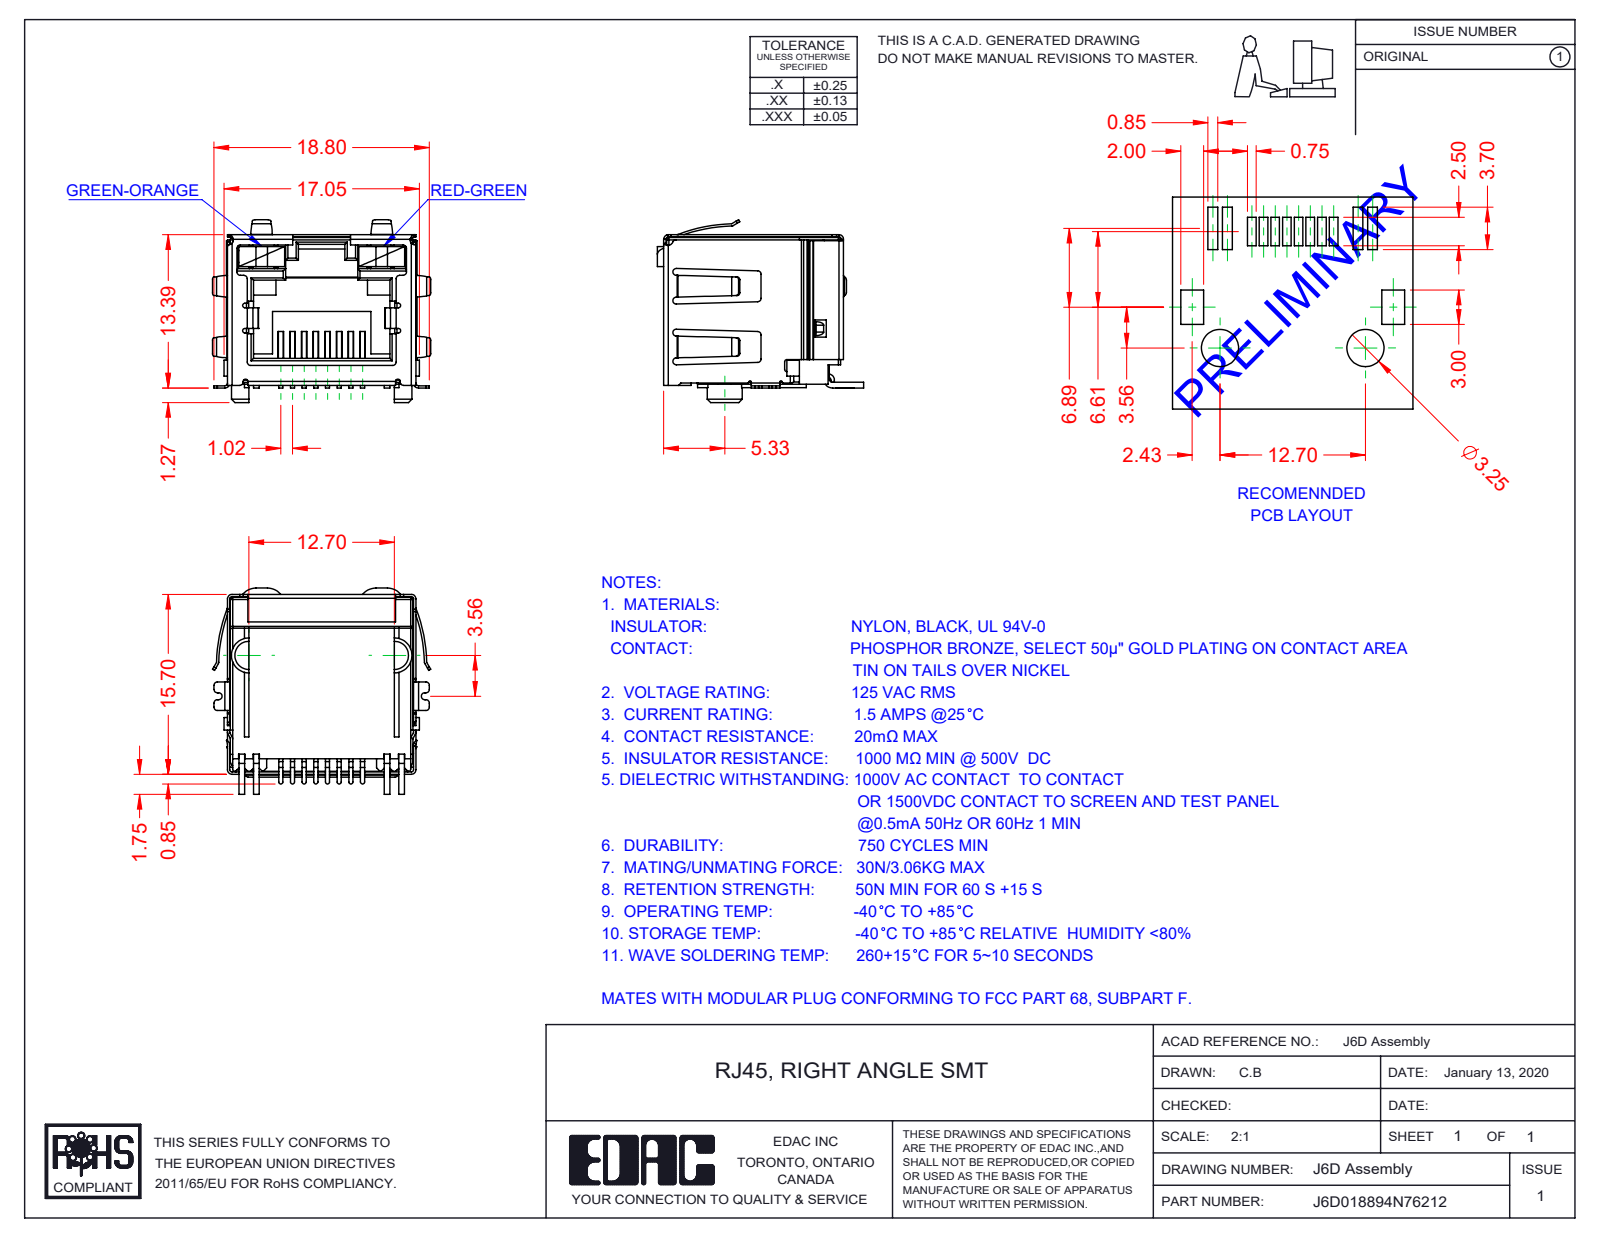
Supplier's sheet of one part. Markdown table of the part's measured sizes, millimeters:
| quantity | value |
| --- | --- |
| part name | J6D018894N76212; 6D LED RH_6-Red-Green; 6D LED LH_7-Green-Orange; 6D Contacts (+2 more) |
| STEP written by | SolidWorks 2016 (CONFIG_CONTROL_DESIGN) |
| units | millimeters |
| bodies | 12 solids, 1034 faces (703 planar, 286 cylindrical, 45 other) |
| overall size | 19.06 × 18 × 15.95 |
| volume | 1 790 mm³ |
| surface area | 4 796 mm² |
| partial cylindrical surfaces (radius × count) | 0.3 × 55, 0.2 × 40, 0.4 × 19, 0.25 × 16, 0.1 × 12, 0.15 × 8, 0.18 × 8, 0.5 × 6 |
| main face-to-face distances | 16, 16.2, 16.25, 2.25, 1, 15.95, 12.8, 0.45, 13.05, 10.6 |
